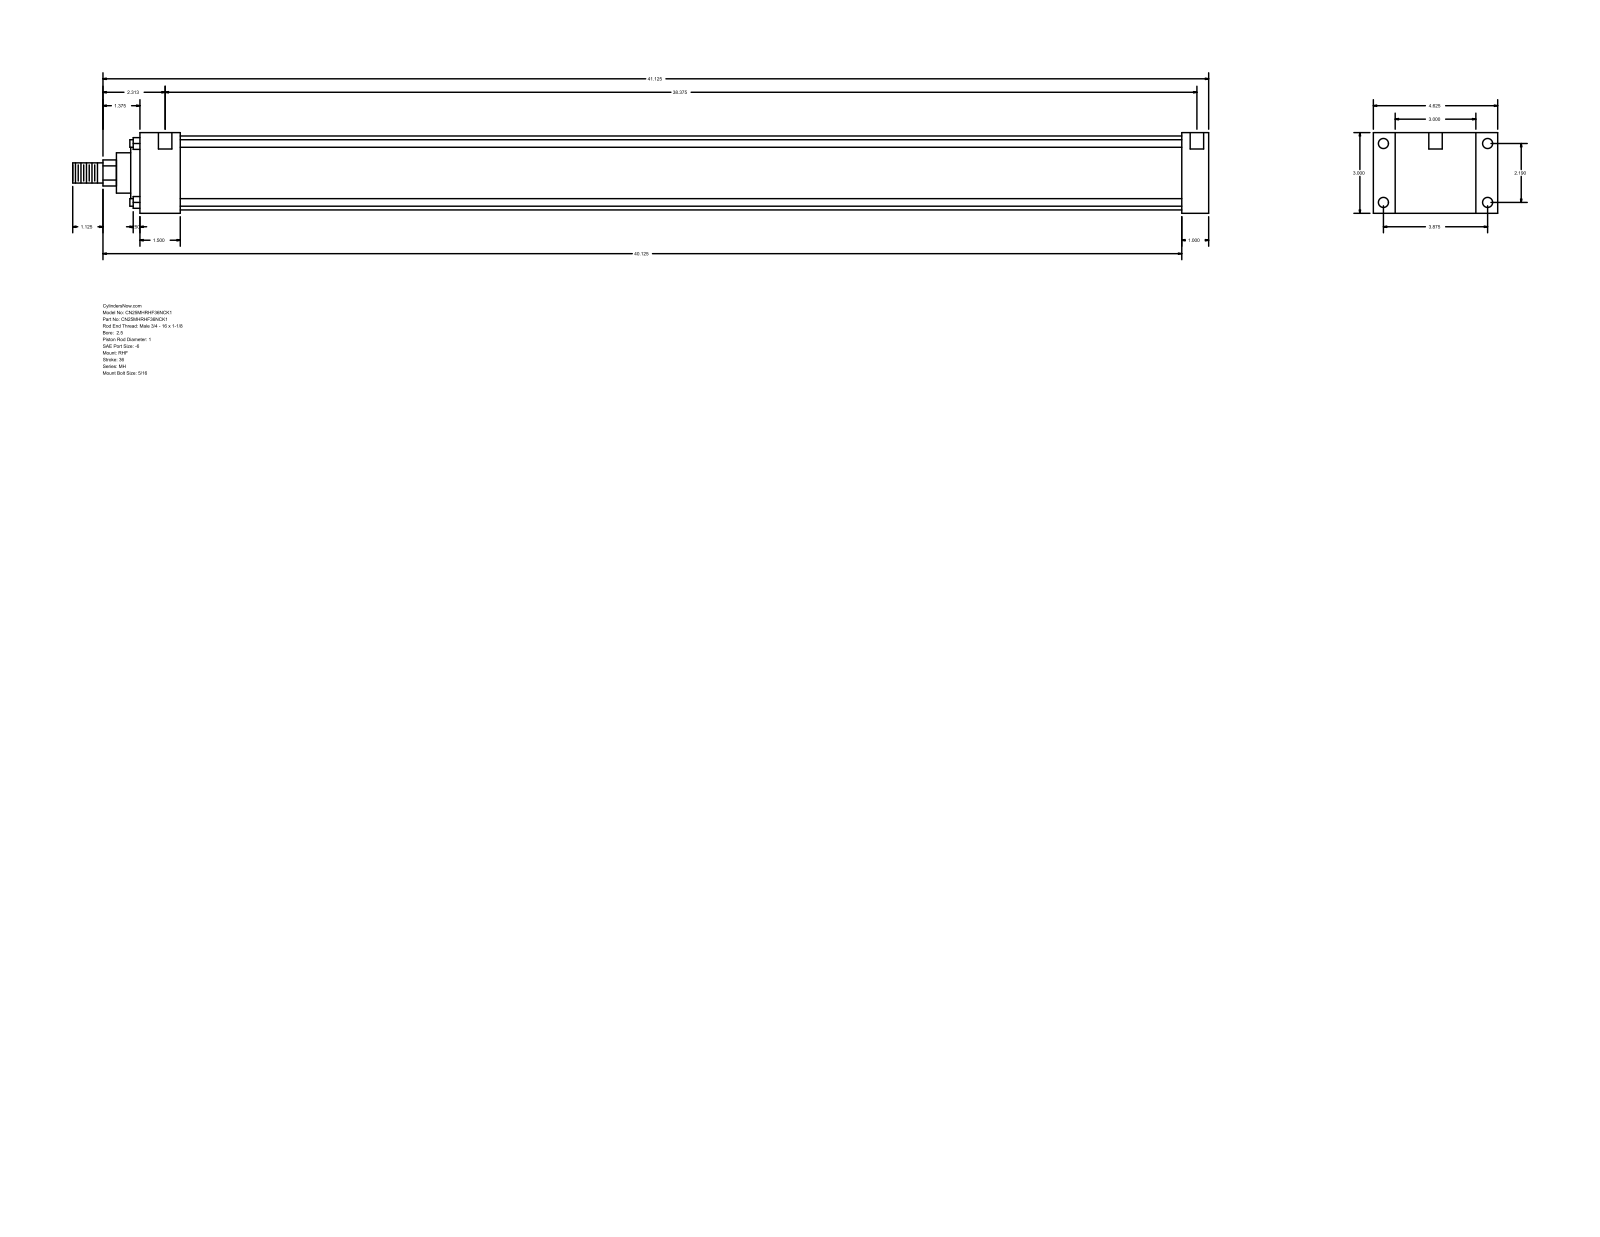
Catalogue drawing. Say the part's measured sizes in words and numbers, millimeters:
The part is named "MH_RHF__0250_1". Its 3-D file was written by "GSSL Pune (CONFIG_CONTROL_DESIGN)". It is 0 solids with 90 faces: 61 planar, 29 cylindrical and 0 other. Overall it measures 1073.15 by 117.47 by 76.2 millimeters. Round holes: 4 of diameter 5.56, 4 of diameter 9.53, 2 of diameter 12.7. Round bosses or shafts: 4 of diameter 7.14, 1 of diameter 69.85, 1 of diameter 60.33, 1 of diameter 38.1, 1 of diameter 25.4, 1 of diameter 19.05. Partial cylindrical surfaces (rounded edges, fillets, slot ends): 1 of radius 12.29. The main face-to-face distances are 76.2, 25.41, 20.64, 96.84, 984.25, 1009.66, 117.48, 38.11, 946.14, 971.55. The hole center spacings are 55.62, 98.42, 113.05, 982.66, 3.18, 4.76, 974.72, 977.9.
